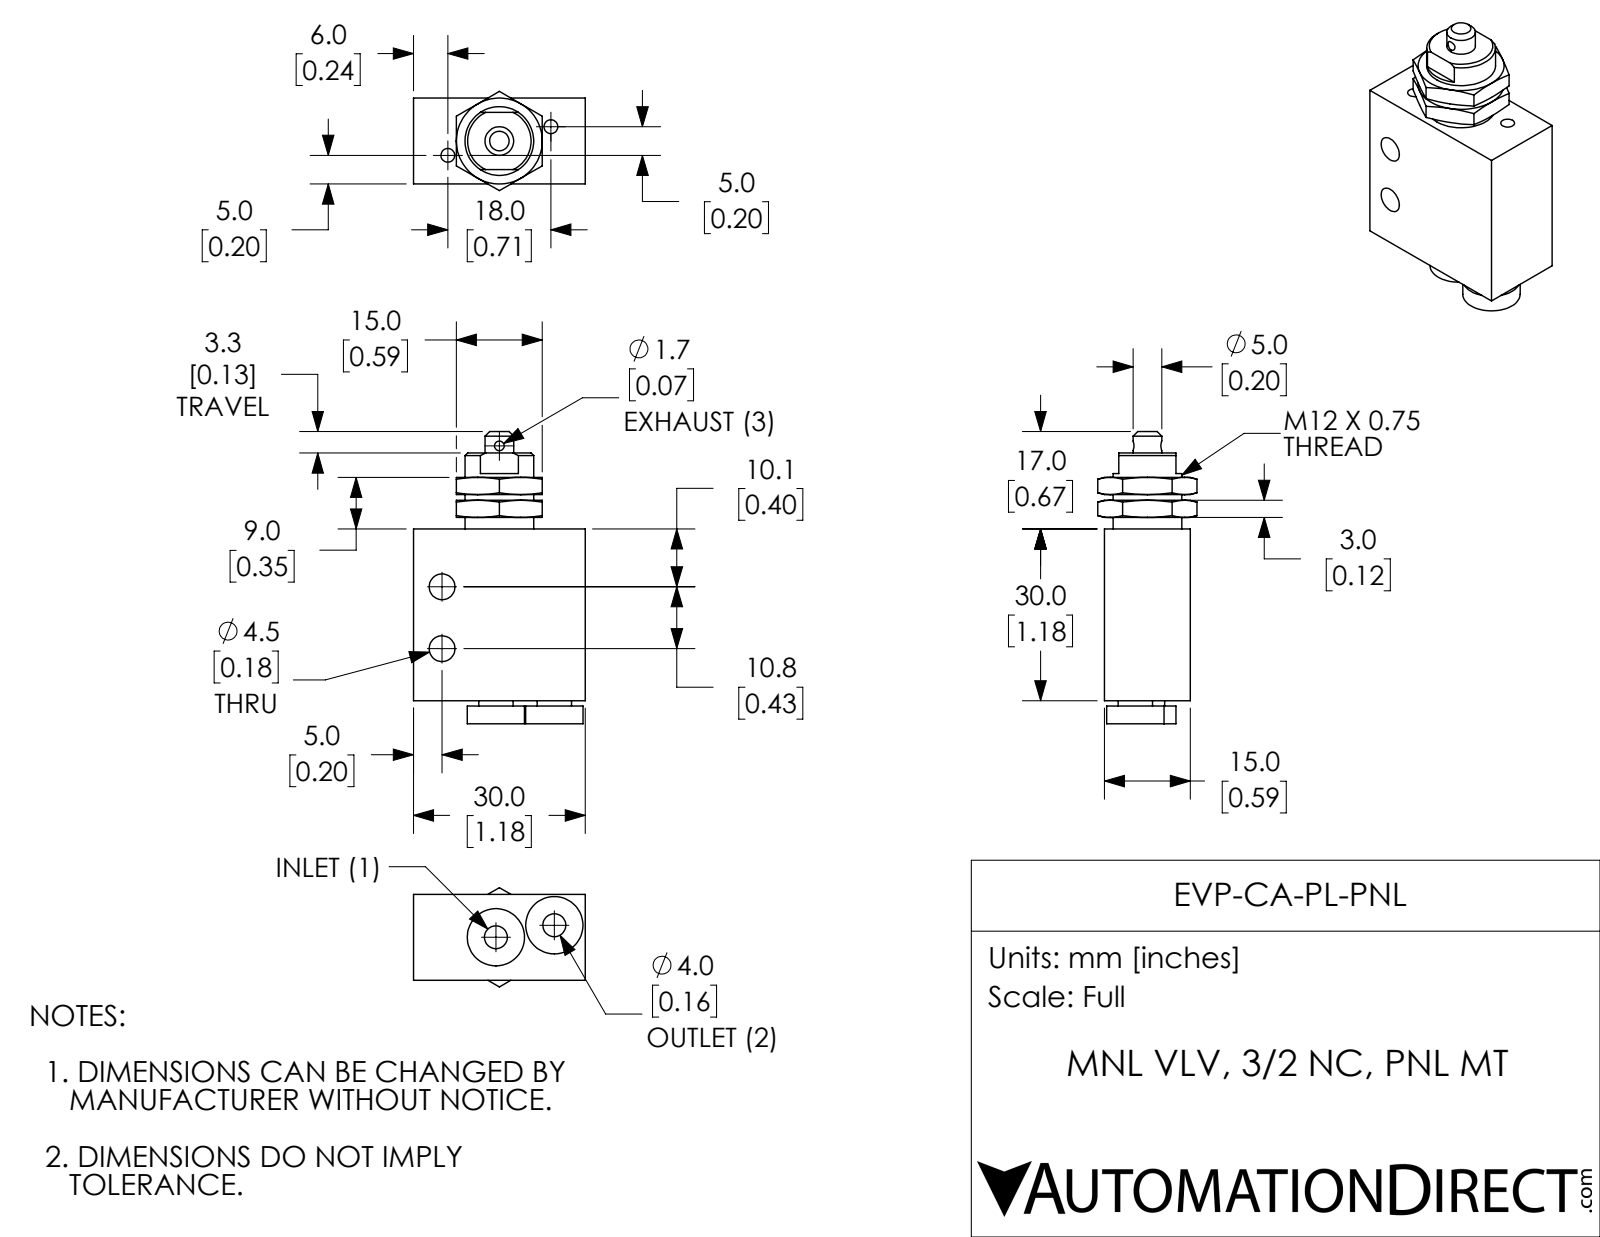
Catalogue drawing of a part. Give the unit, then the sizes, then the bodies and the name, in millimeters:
Units: millimetres
Overall size (bounding box): 51 × 30 × 17.3
Round holes (diameter × count): ⌀2.4 ×2, ⌀4 ×2, ⌀4.5 ×2, ⌀1.7 ×1
Round bosses / shafts (diameter × count): ⌀10 ×2, ⌀6 ×2, ⌀12 ×1, ⌀5 ×1
Main face-to-face distances: 15, 30, 4, 34, 39, 36, 3, 3.1, 0.9, 30.9
Hole centre spacings: 4.6, 8.8, 9.9, 10.4, 10.8, 18.6, 18.7, 26.5
Volume: 15 400 mm³ · Surface area: 5 506 mm²
Bodies: 1 solid, 97 faces (36 planar, 30 cylindrical, 31 other)
Part name (STEP PRODUCT): EVP-CA-PL-PNL
STEP written by: SolidWorks 2017 (AUTOMOTIVE_DESIGN)
